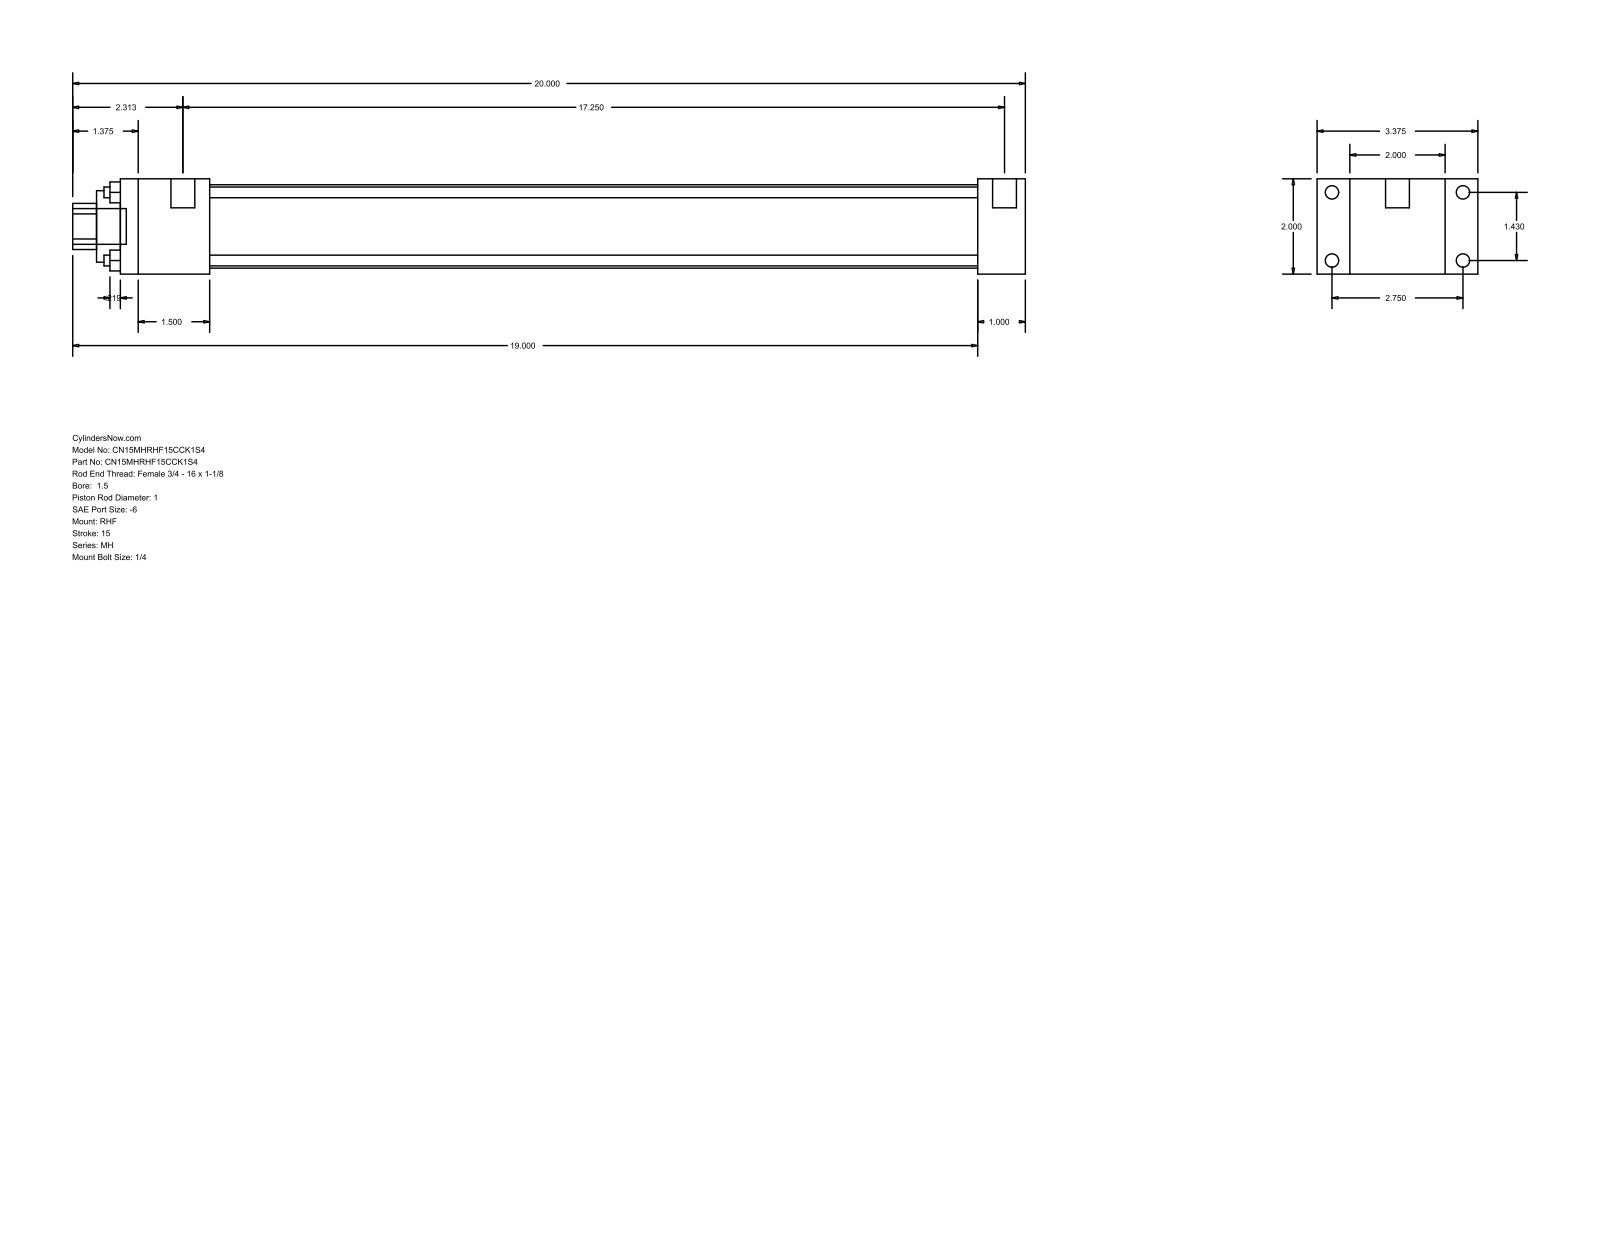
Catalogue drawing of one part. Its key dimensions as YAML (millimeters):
part_name: "MH_RHF__0150_1"
step_written_by: "GSSL Pune (CONFIG_CONTROL_DESIGN)"
units: millimeters
bodies: {solids: 0, faces: 88, planar: 60, cylindrical: 28, other: 0}
overall_size: [508, 85.72, 50.8]
round_holes:
  - {diameter: 5.71, count: 4}
  - {diameter: 25.4, count: 1}
  - {diameter: 38.1, count: 1}
  - {diameter: 44.45, count: 1}
round_bosses_or_shafts:
  - {diameter: 7.14, count: 4}
  - {diameter: 5.56, count: 4}
  - {diameter: 12.7, count: 2}
  - {diameter: 19.05, count: 1}
partial_cylinders:
  - {radius: 12.29, count: 1}
face_to_face_distances: [50.8, 25.4, 17.46, 68.26, 85.72, 482.6, 457.2, 47.63, 409.57, 434.97]
hole_center_spacings: [25.68, 36.32, 51.36]
